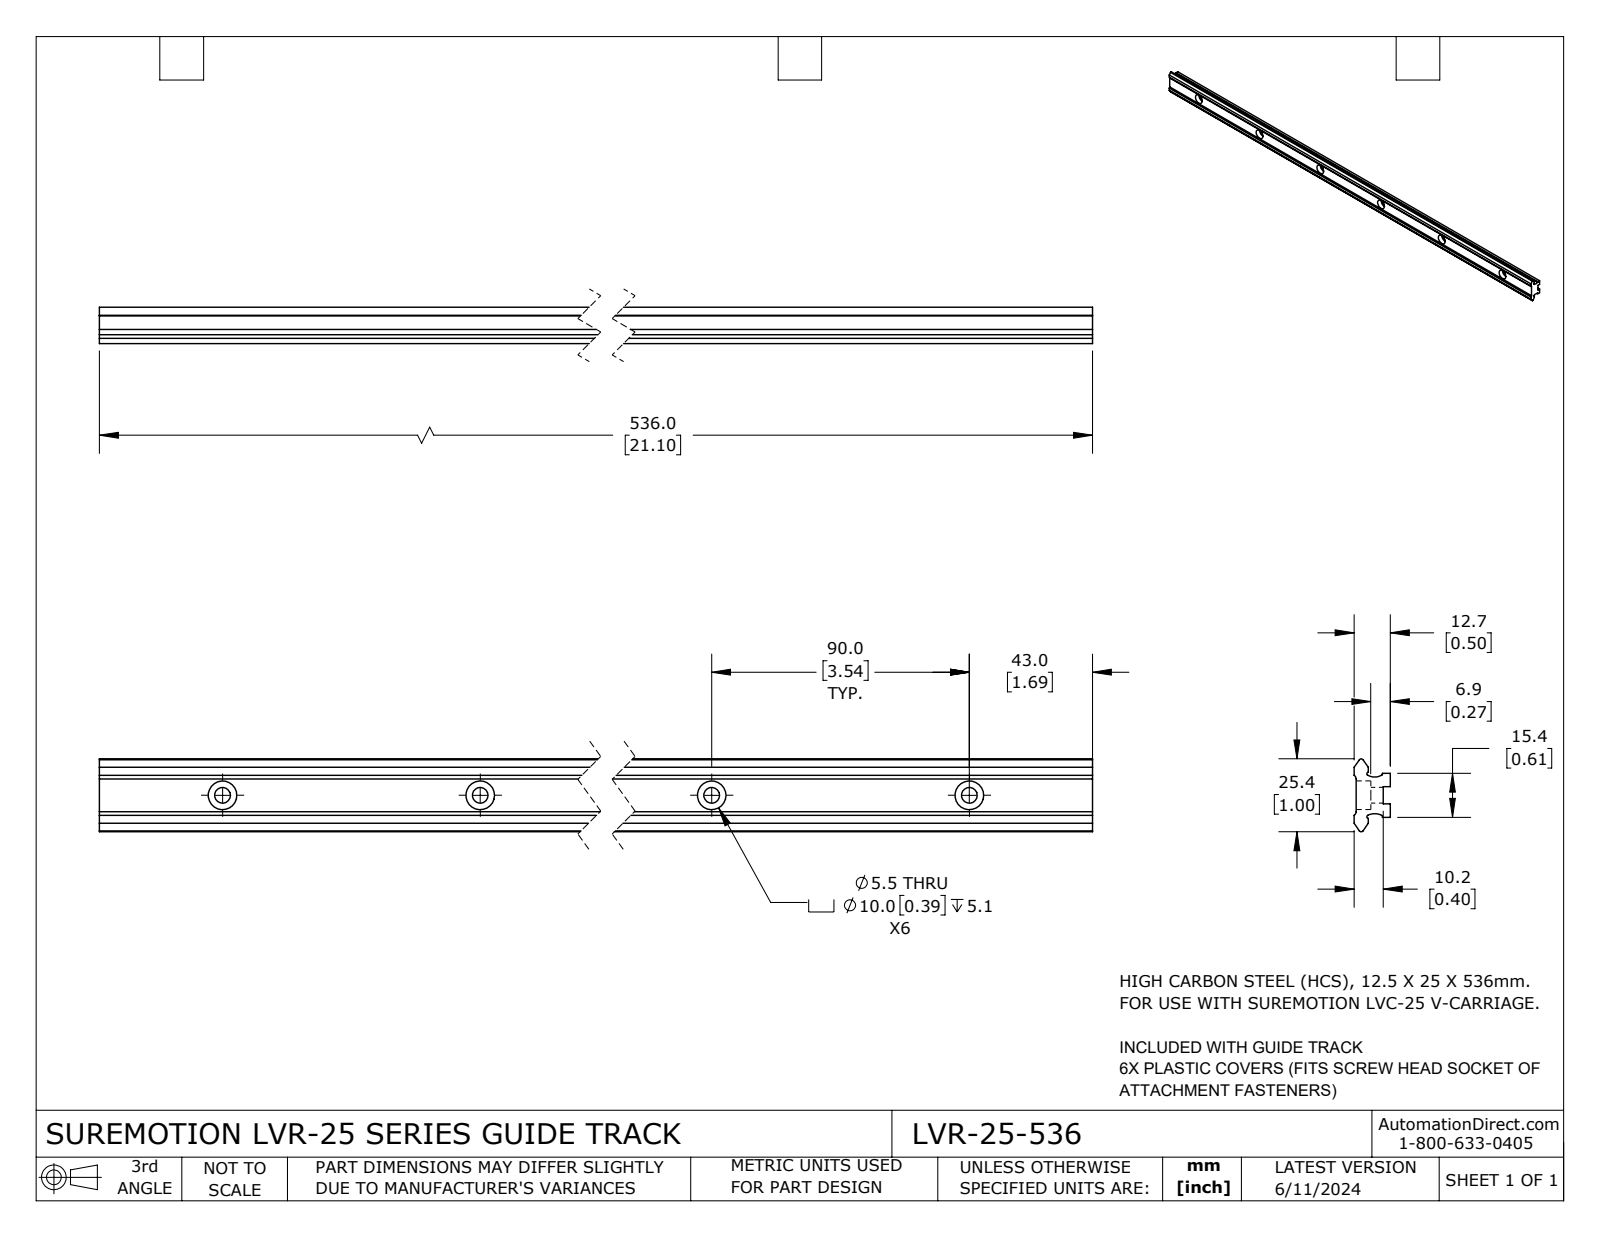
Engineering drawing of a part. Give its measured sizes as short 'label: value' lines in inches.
name: LVR-25-536
written by: SolidWorks 2023 (CONFIG_CONTROL_DESIGN)
unit: in
bodies: 1 solid, 60 faces (24 planar, 36 cylindrical, 0 other)
size: 21.102 × 1.002 × 0.498
volume: 6.235 in³; area: 68.71 in²
holes: 6× ⌀0.217, 6× ⌀0.394
rounds: 4× R0.022, 2× R0.03, 2× R0.059, 2× R0.206
face distances: 0.471, 0.6, 0.098, 0.372, 0.498, 0.4, 0.028, 0.185, 0.421, 0.304
hole spacings: 3.543, 7.087, 10.63, 14.173, 17.717
